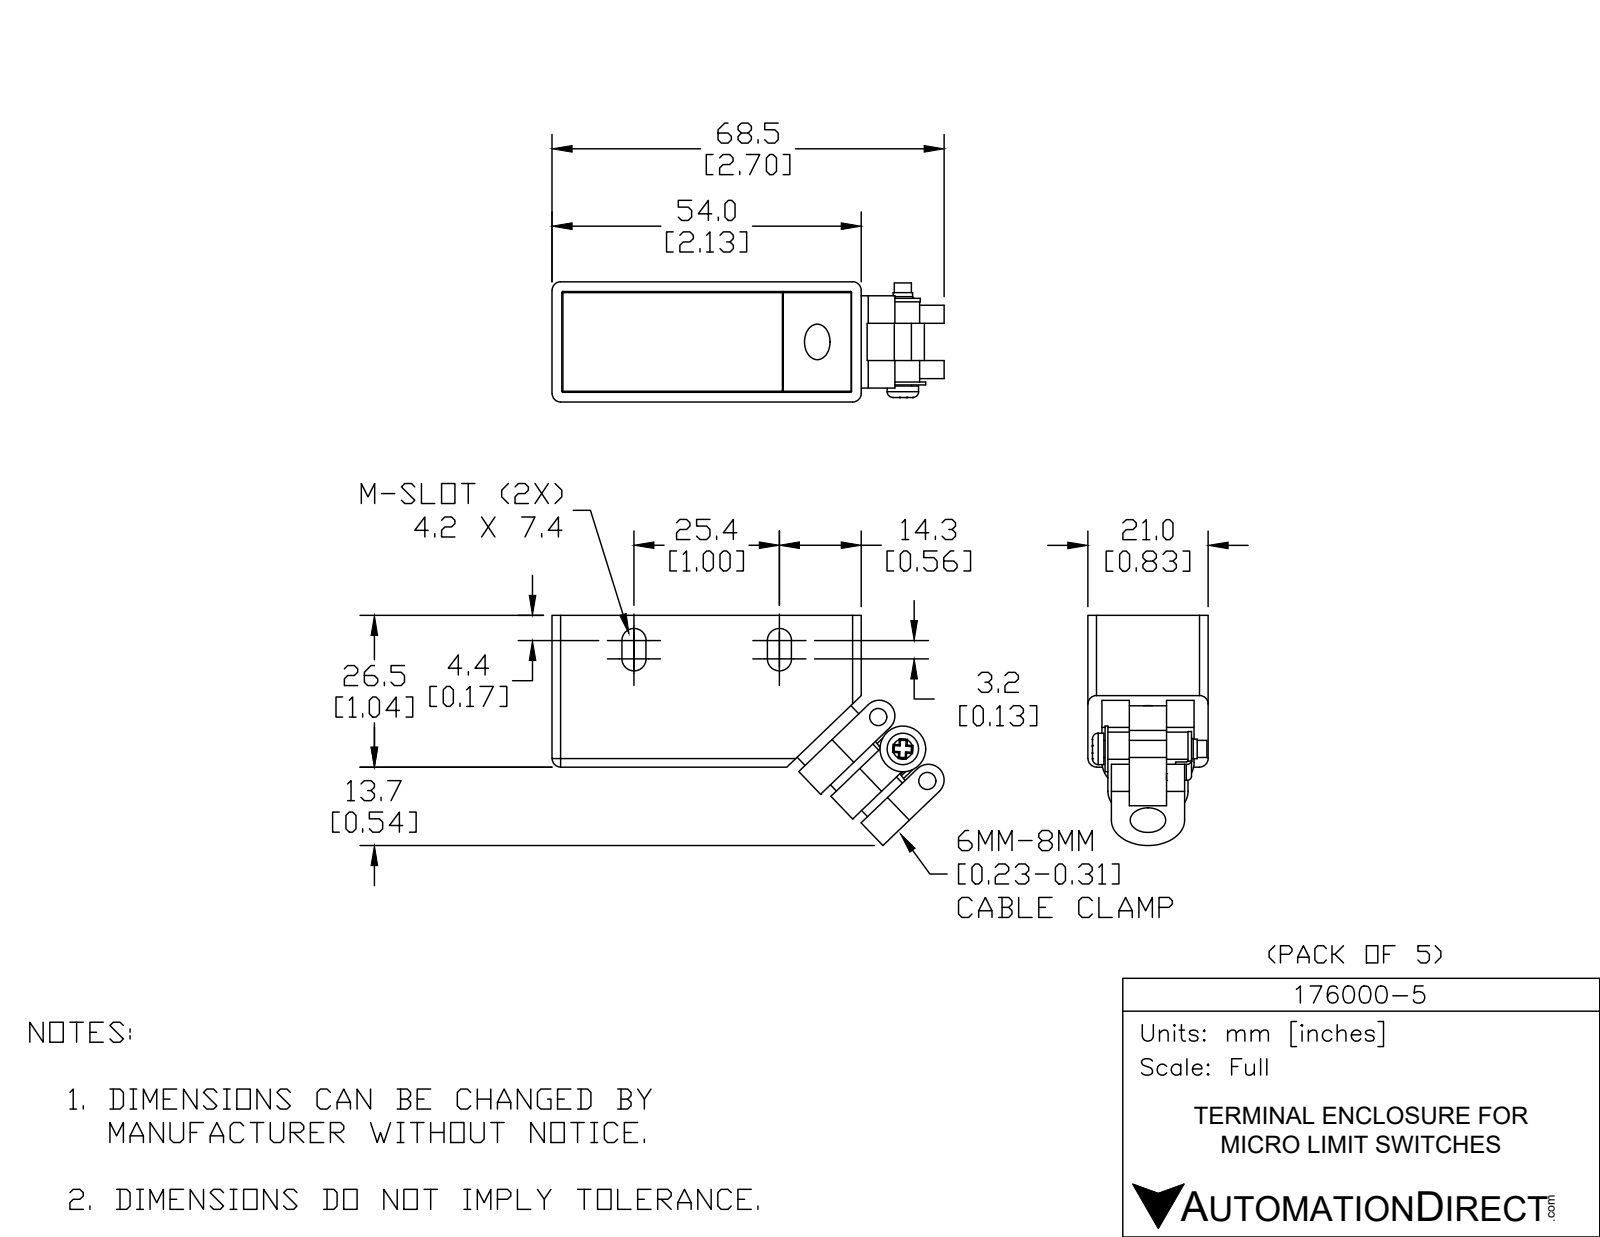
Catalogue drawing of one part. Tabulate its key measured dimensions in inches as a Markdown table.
| quantity | value |
| --- | --- |
| part name | 176000-1 |
| STEP written by | SolidWorks 2018 (AUTOMOTIVE_DESIGN) |
| units | inches |
| bodies | 4 solids, 179 faces (84 planar, 68 cylindrical, 27 other) |
| overall size | 2.696 × 1.582 × 0.827 |
| volume | 0.628 in³ |
| surface area | 18.12 in² |
| round holes (diameter × count) | 0.118 × 3, 0.098 × 1, 0.126 × 1, 0.244 × 1 |
| round bosses / shafts (diameter × count) | 0.512 × 1, 0.445 × 1, 0.315 × 1, 0.217 × 1, 0.134 × 1 |
| partial cylindrical surfaces (radius × count) | 0.008 × 19, 0.059 × 7, 0.083 × 4, 0.108 × 3, 0.012 × 2, 0.035 × 2, 0.118 × 1, 0.191 × 1 |
| main face-to-face distances | 0.067, 0.76, 0.827, 0.693, 2.059, 0.276, 0.551, 2.126, 0.217, 1.043 |
| hole center spacings | 0.277, 0.277, 0.554 |
